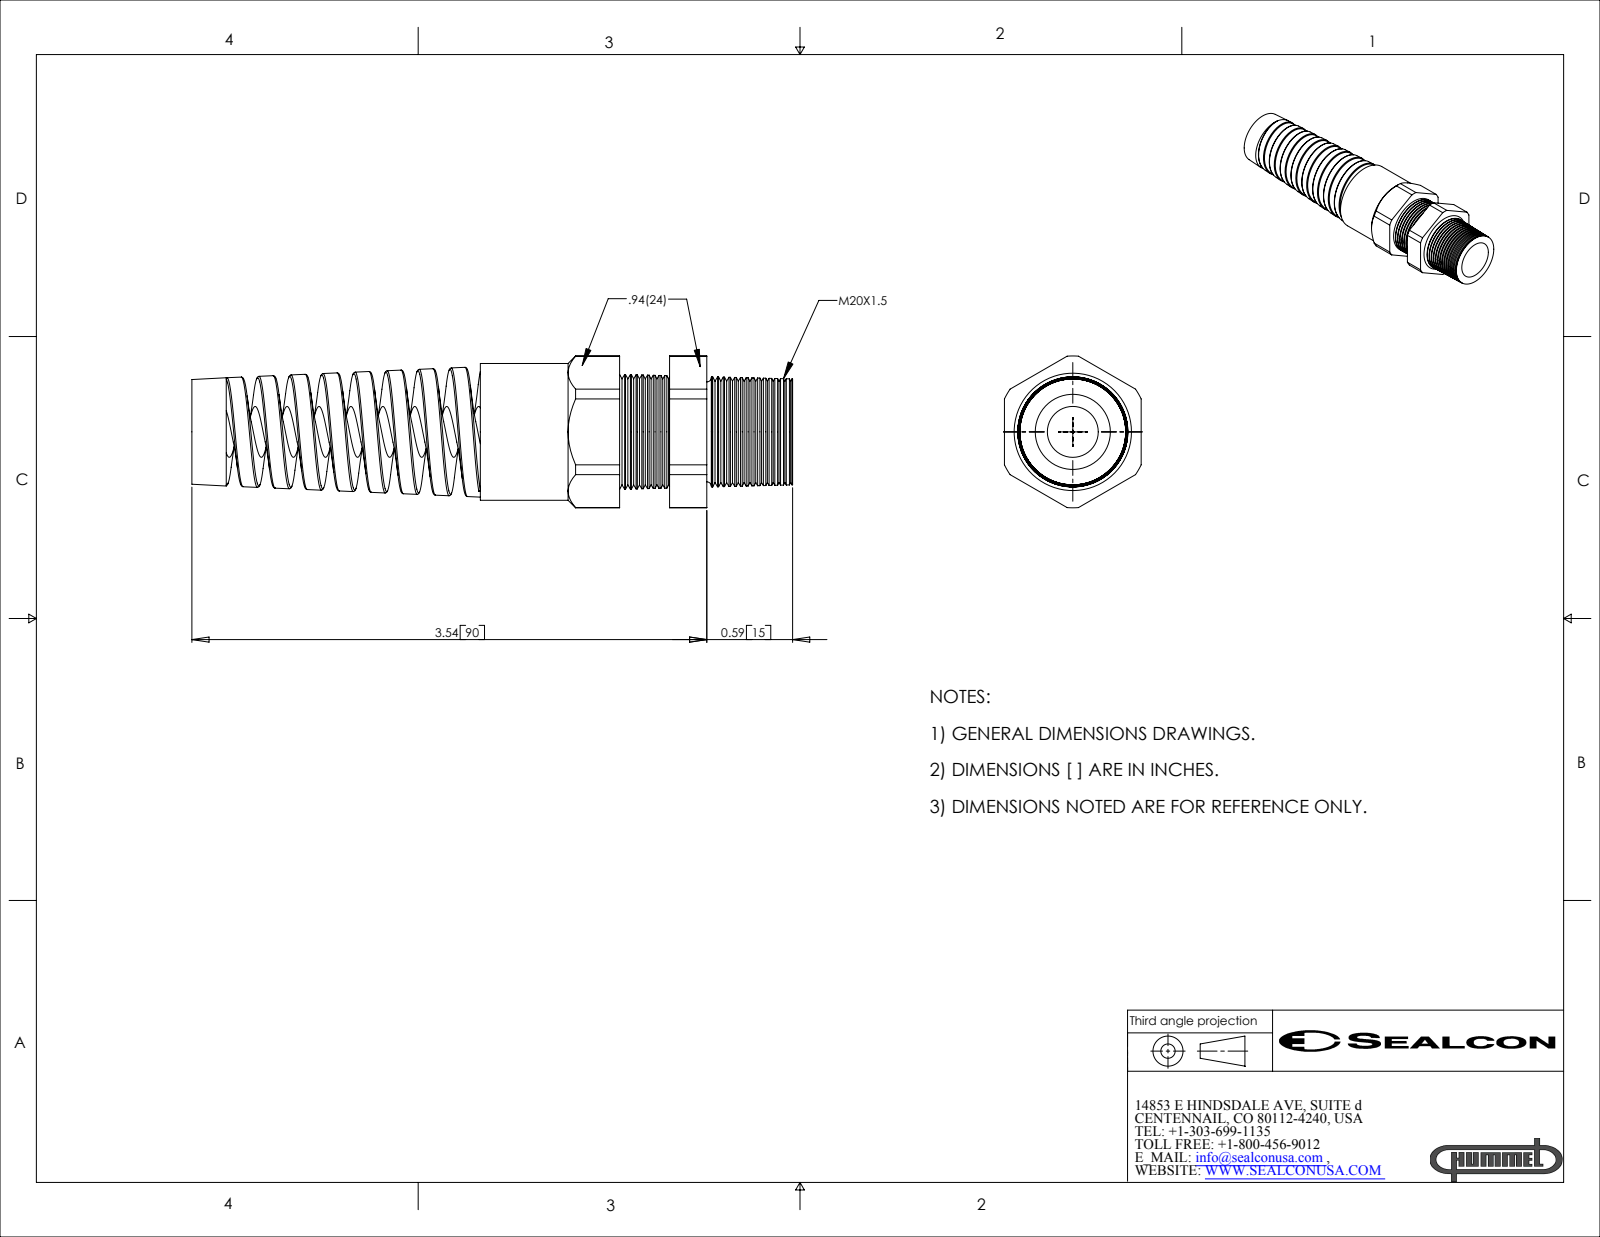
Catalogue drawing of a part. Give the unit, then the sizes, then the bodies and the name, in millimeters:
Units: millimetres
Overall size (bounding box): 104.9 × 26.5 × 23.9
Round holes (diameter × count): ⌀8.9 ×1, ⌀9.5 ×1
Round bosses / shafts (diameter × count): ⌀23.9 ×1, ⌀17.4 ×1
Partial cylindrical surfaces — rounded edges, fillets, slot ends (radius × count): R13.3 ×1
Main face-to-face distances: 23.9, 65.7, 50.4, 15.3, 83.4, 33, 17.7, 74.7, 24.3, 9
Volume: 25 600 mm³ · Surface area: 15 650 mm²
Bodies: 2 solids, 248 faces (25 planar, 41 cylindrical, 182 other)
Part name (STEP PRODUCT): CF20DR-GY
STEP written by: SolidWorks 2007 (CONFIG_CONTROL_DESIGN)
